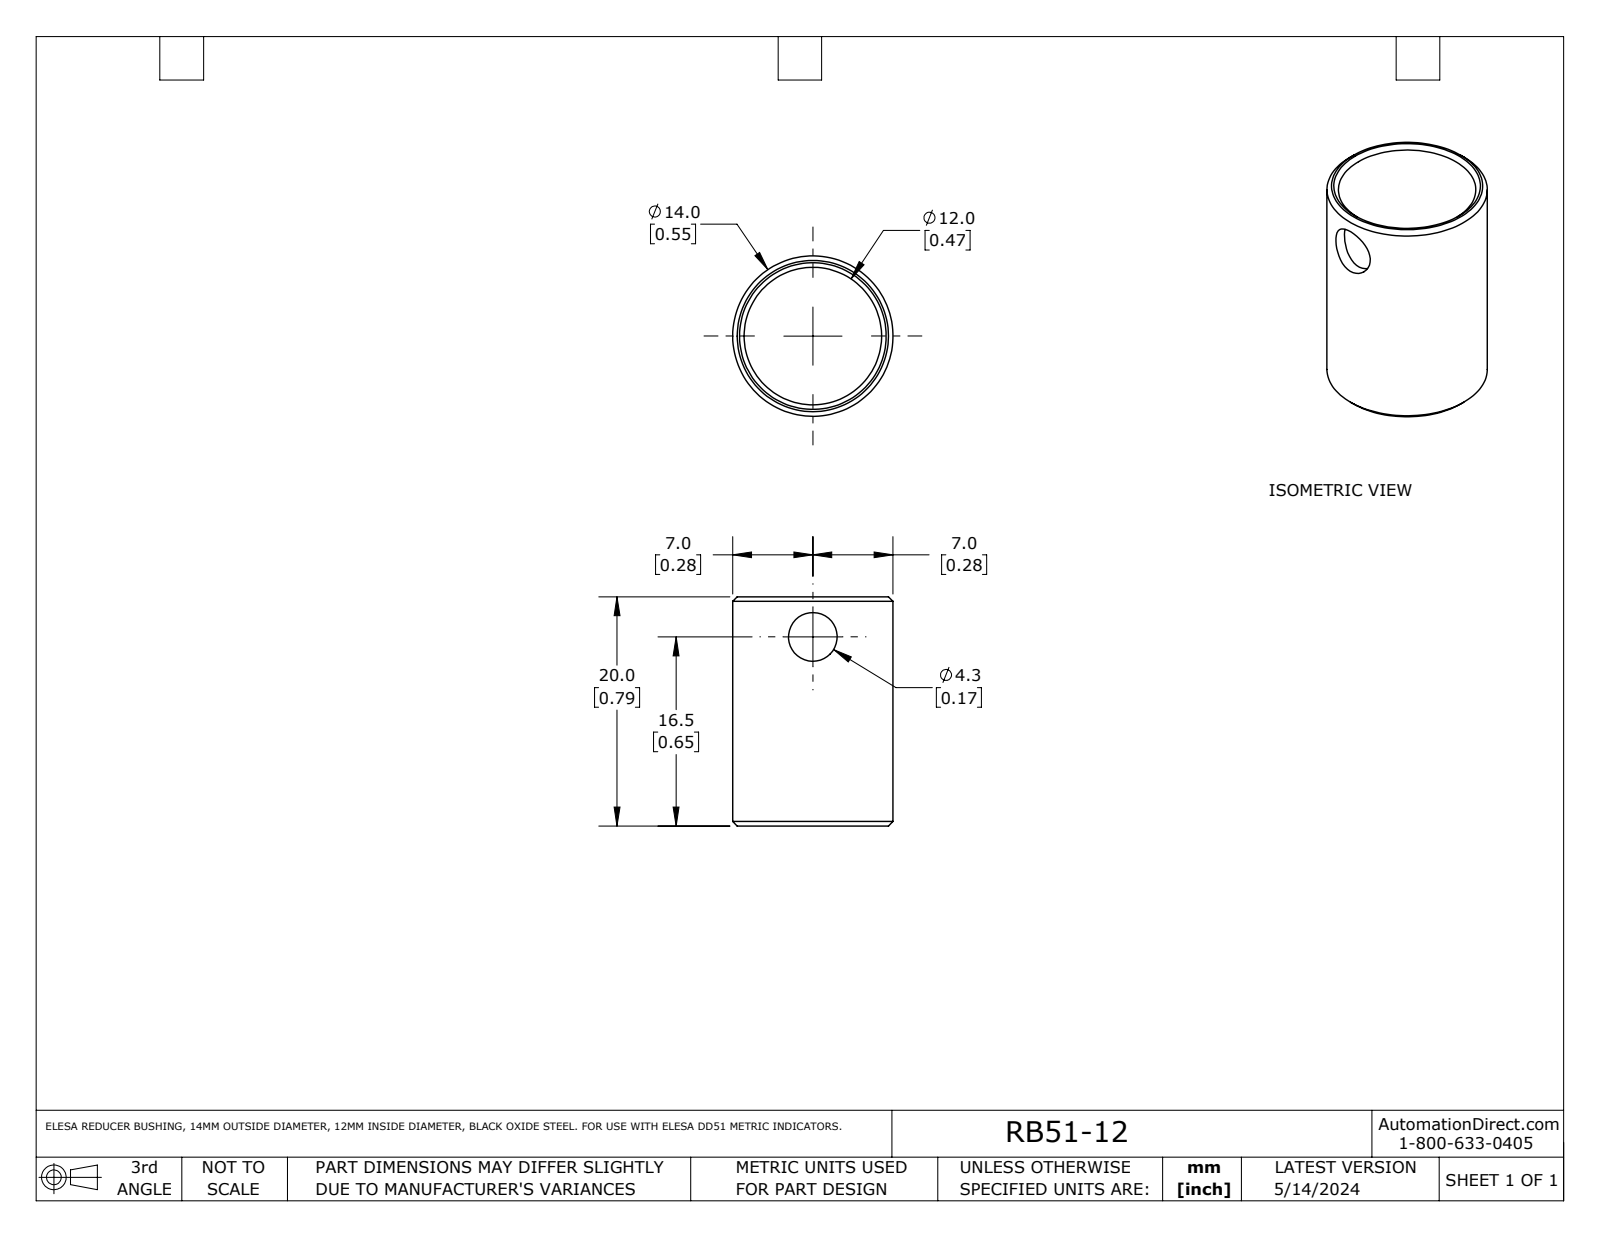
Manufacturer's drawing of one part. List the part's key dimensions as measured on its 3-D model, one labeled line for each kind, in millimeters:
Part name (STEP PRODUCT): RB51-12
STEP written by: SolidWorks 2023 (AUTOMOTIVE_DESIGN)
Units: millimetres
Bodies: 1 solid, 9 faces (2 planar, 3 cylindrical, 4 other)
Overall size (bounding box): 20 × 14 × 14
Volume: 790 mm³ · Surface area: 1 662 mm²
Round holes (diameter × count): ⌀4.2 ×1, ⌀12 ×1
Round bosses / shafts (diameter × count): ⌀14 ×1
Main face-to-face distances: 20
